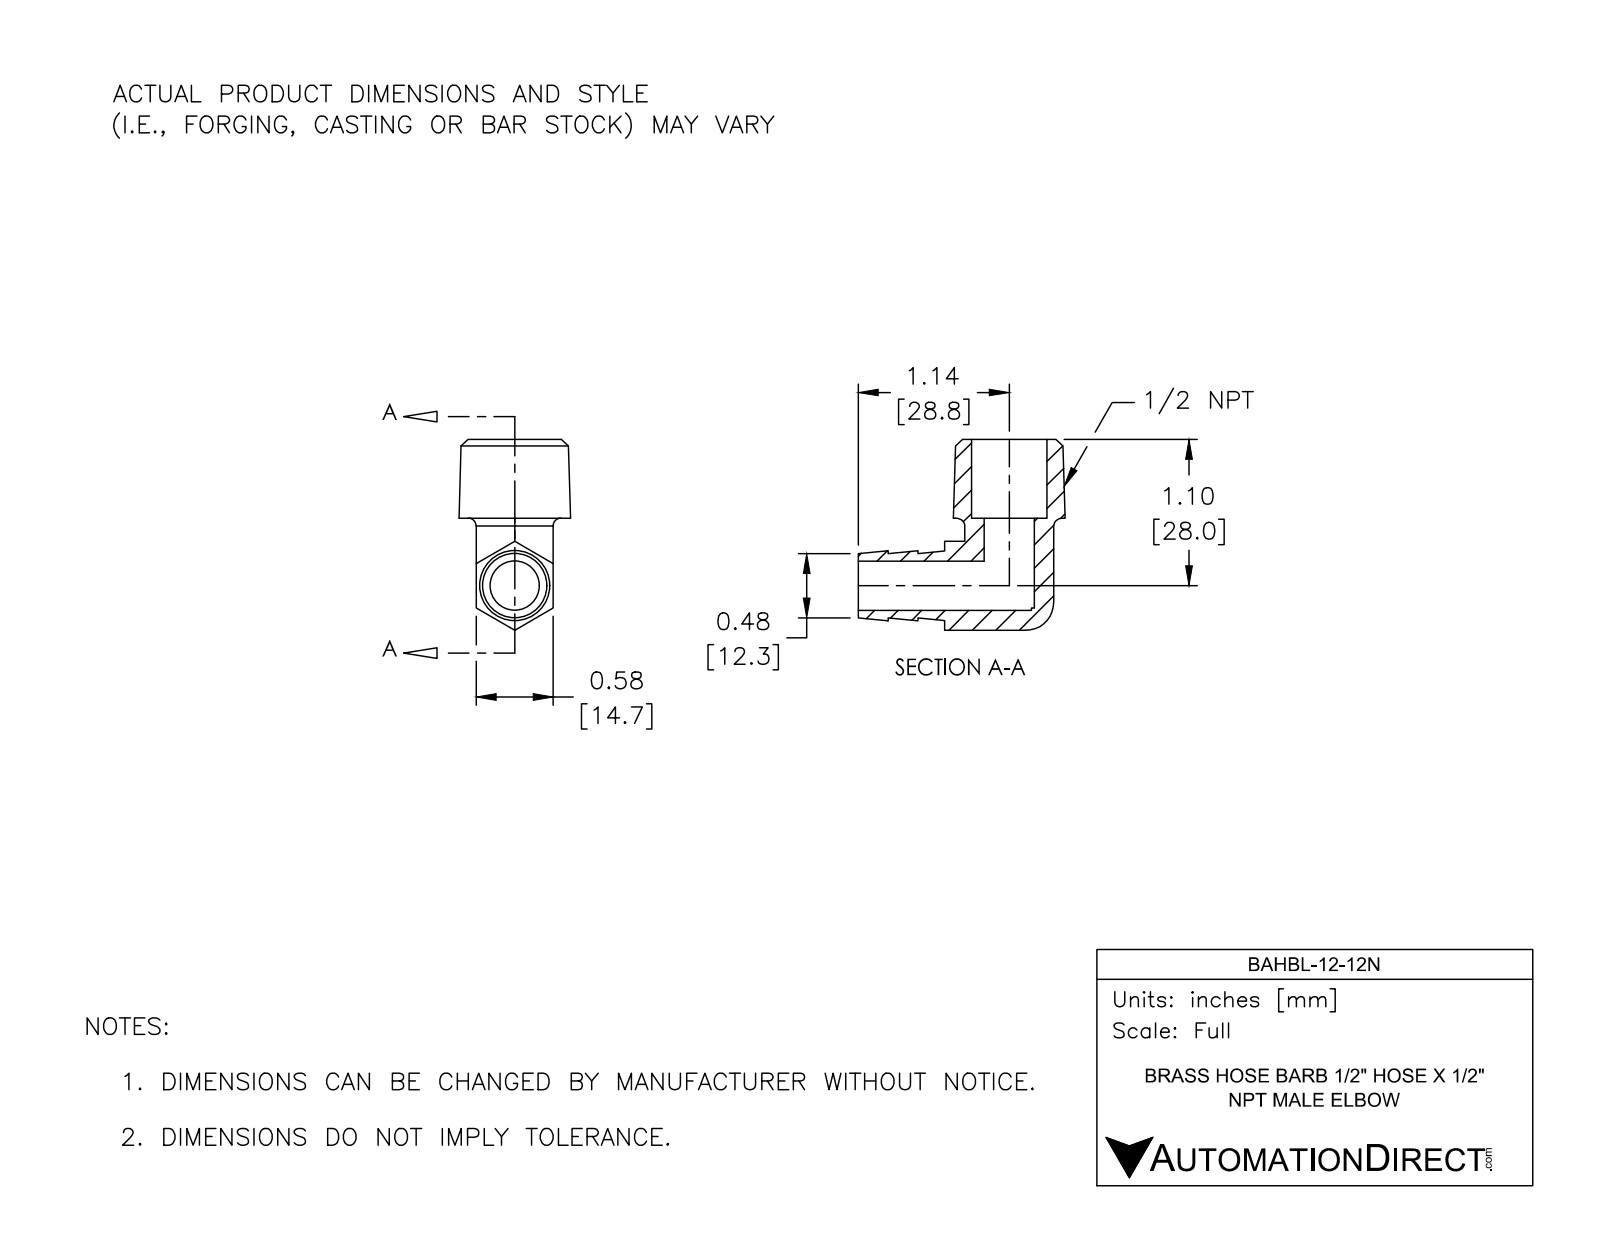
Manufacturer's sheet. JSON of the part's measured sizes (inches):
{"part_name": "BAHBL-12-12N", "step_written_by": "SolidWorks 2017 (AUTOMOTIVE_DESIGN)", "units": "inches", "bodies": {"solids": 1, "faces": 48, "planar": 21, "cylindrical": 17, "other": 10}, "overall_size": [1.556, 1.435, 0.84], "volume_in3": 0.394, "surface_area_in2": 8.305, "round_holes": [[0.371, 1], [0.376, 1], [0.568, 1]], "partial_cylinders_radius": [[0.06, 6], [0.25, 2]], "face_to_face_distances": [0.579, 0.579, 0.592, 0.649, 0.224, 0.676, 1.268, 0.654, 1.303, 0.855]}
